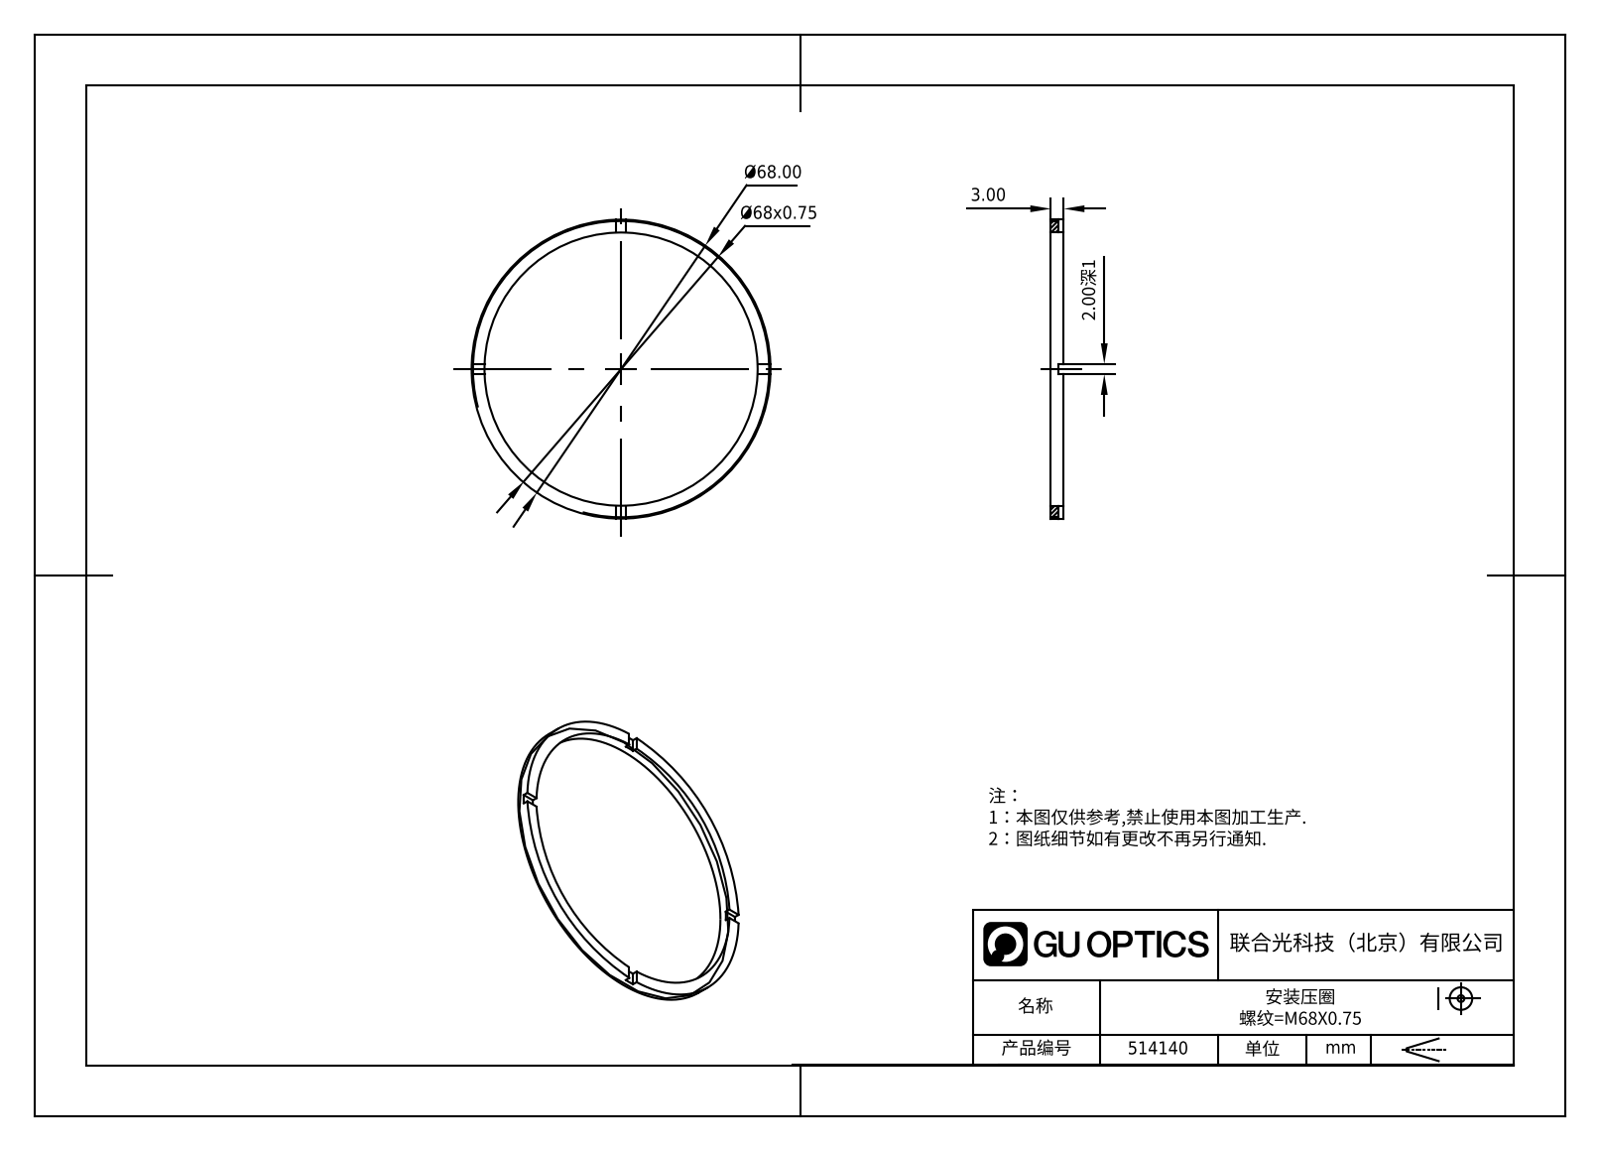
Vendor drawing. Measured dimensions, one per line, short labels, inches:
name: 514140
written by: SolidWorks 2020 (CONFIG_CONTROL_DESIGN)
unit: in
bodies: 1 solid, 21 faces (17 planar, 4 cylindrical, 0 other)
size: 2.677 × 2.677 × 0.118
volume: 0.093 in³; area: 3.515 in²
holes: 1× ⌀2.48
bosses: 1× ⌀2.677
face distances: 0.118, 0.079, 0.039
